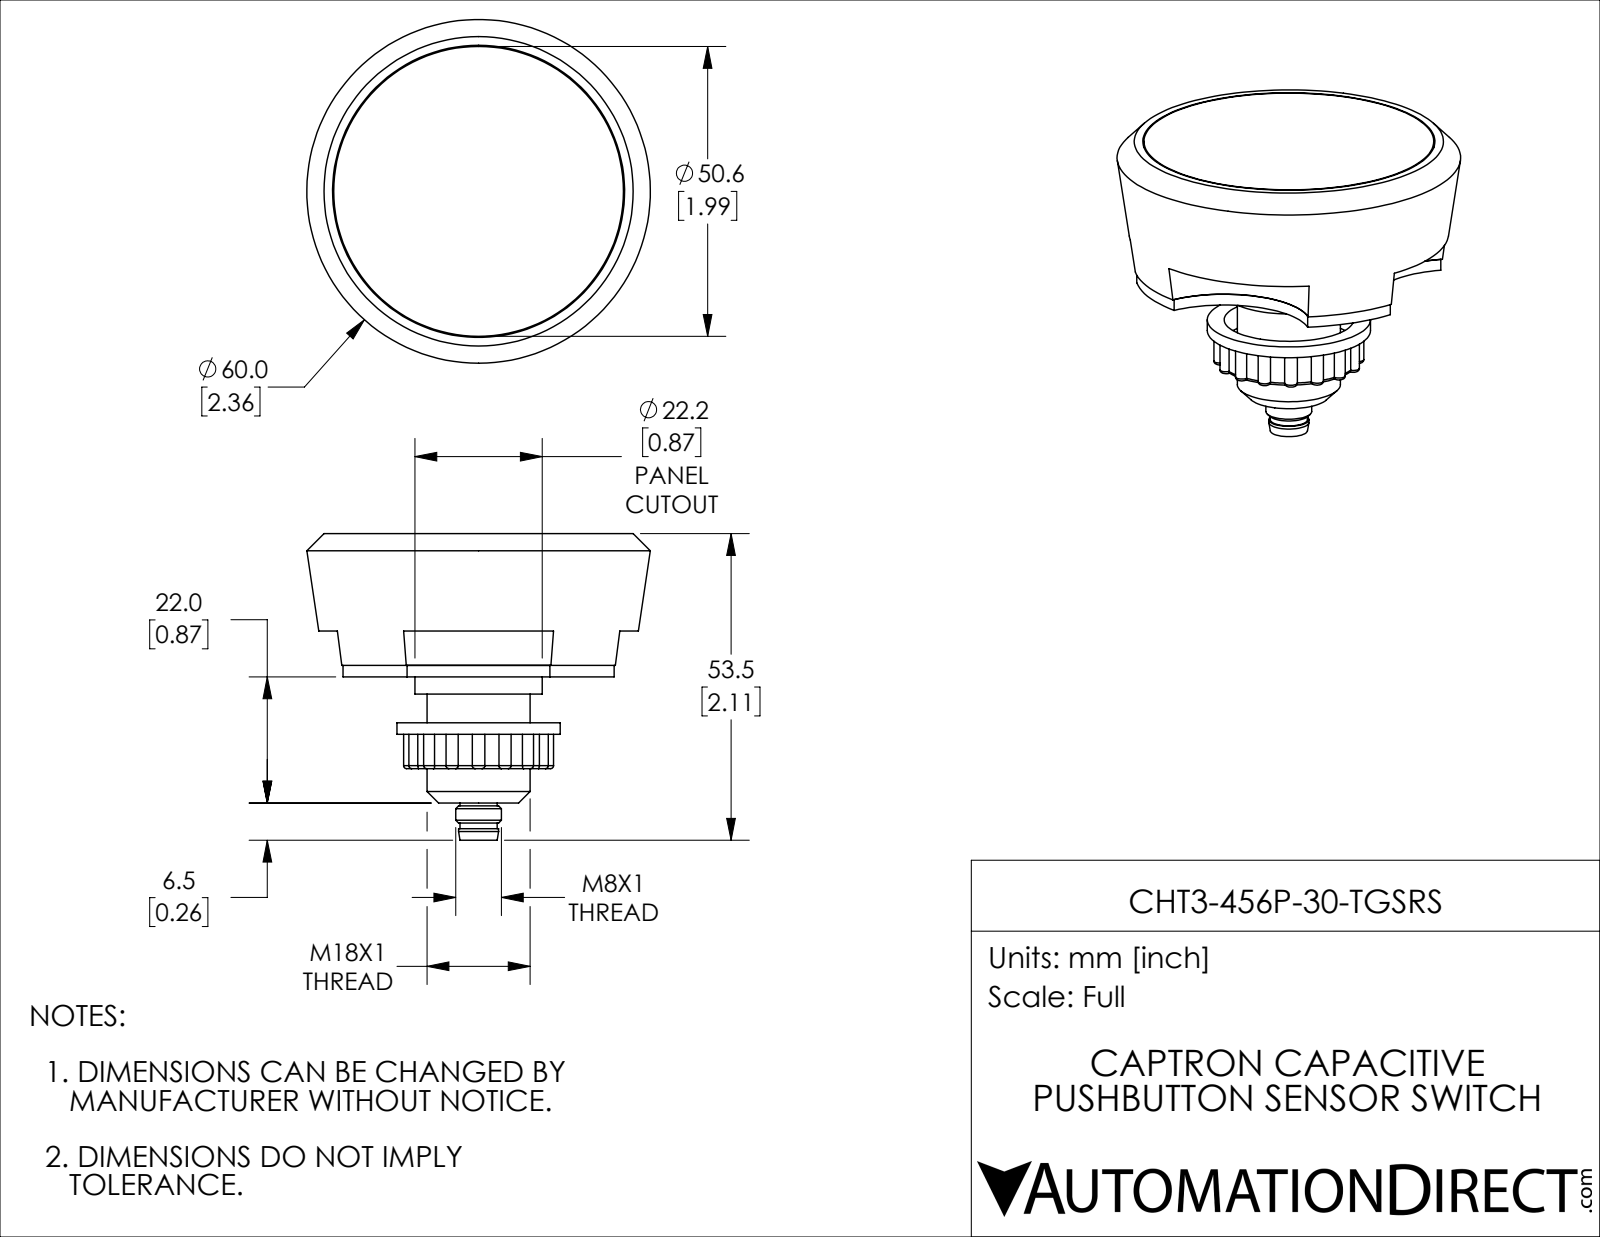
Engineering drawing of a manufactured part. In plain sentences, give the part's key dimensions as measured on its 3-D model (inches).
The part is named "CHT3-456P-30-TGSRS". Its 3-D file was written by "SolidWorks 2019 (CONFIG_CONTROL_DESIGN)". It is 9 solids with 197 faces: 27 planar, 95 cylindrical and 75 other. Overall it measures 2.362 by 2.362 by 2.106 inches. Its volume is 3.903 cubic inches and its surface area 31.91 square inches. Round holes: 1 of diameter 0.236, 1 of diameter 0.669, 1 of diameter 0.89, 1 of diameter 2.008. Round bosses or shafts: 4 of diameter 0.039, 1 of diameter 1.992, 1 of diameter 1.122, 1 of diameter 0.874, 1 of diameter 0.709, 1 of diameter 0.315, 1 of diameter 0.276, 1 of diameter 0.256. Partial cylindrical surfaces (rounded edges, fillets, slot ends): 16 of radius 0.043, 4 of radius 0.591, 1 of radius 0.472, 1 of radius 1.053. The main face-to-face distances are 0.906, 0.795, 0.11, 0.02, 0.815, 0.091, 0.079, 0.315, 0.874, 0.894.
